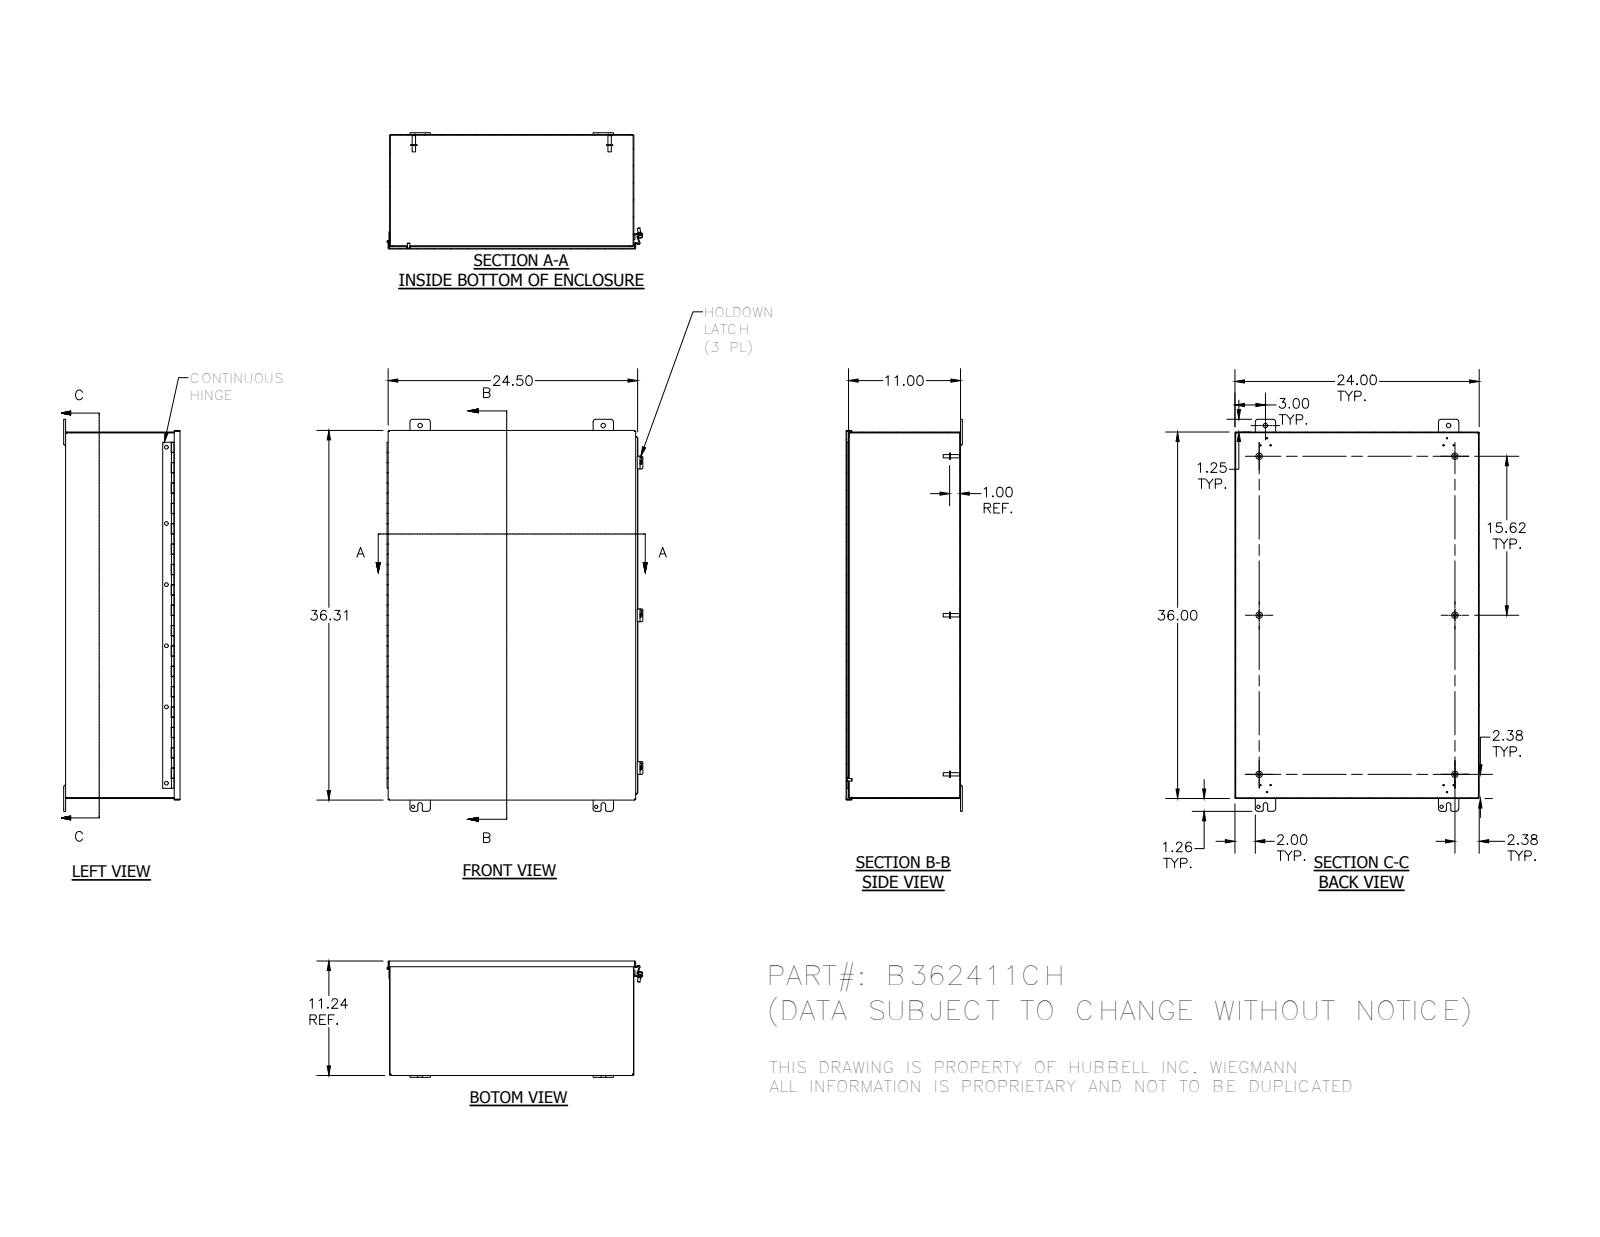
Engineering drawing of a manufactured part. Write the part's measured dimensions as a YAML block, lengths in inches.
part_name: "B362411CH; B362411CHBKP; B3624CHLID; H6010103 (+8 more)"
step_written_by: "Autodesk Inventor 2012 (AUTOMOTIVE_DESIGN)"
units: inches
bodies: {solids: 25, faces: 838, planar: 519, cylindrical: 241, other: 78}
overall_size: [38.505, 25.136, 11.423]
volume: 242.4
surface_area: 6556
round_holes:
  - {diameter: 0.11, count: 6}
  - {diameter: 0.375, count: 6}
  - {diameter: 0.313, count: 4}
  - {diameter: 0.438, count: 4}
  - {diameter: 0.196, count: 3}
  - {diameter: 0.125, count: 1}
  - {diameter: 0.125, count: 1}
round_bosses_or_shafts:
  - {diameter: 0.625, count: 6}
  - {diameter: 0.33, count: 6}
  - {diameter: 0.25, count: 5}
  - {diameter: 0.41, count: 3}
  - {diameter: 0.344, count: 3}
  - {diameter: 0.337, count: 1}
  - {diameter: 0.12, count: 1}
partial_cylinders:
  - {radius: 0.125, count: 20}
  - {radius: 0.25, count: 16}
  - {radius: 0.063, count: 12}
  - {radius: 0.031, count: 8}
  - {radius: 0.07, count: 8}
  - {radius: 0.105, count: 8}
  - {radius: 0.133, count: 6}
  - {radius: 0.016, count: 5}
face_to_face_distances: [0.074, 11.169, 11.243, 11.095, 23.926, 35.926, 24, 23.852, 36, 35.852]
hole_center_spacings: [18, 15, 0.75, 6, 1.134, 1.593, 1.593, 1.881]
